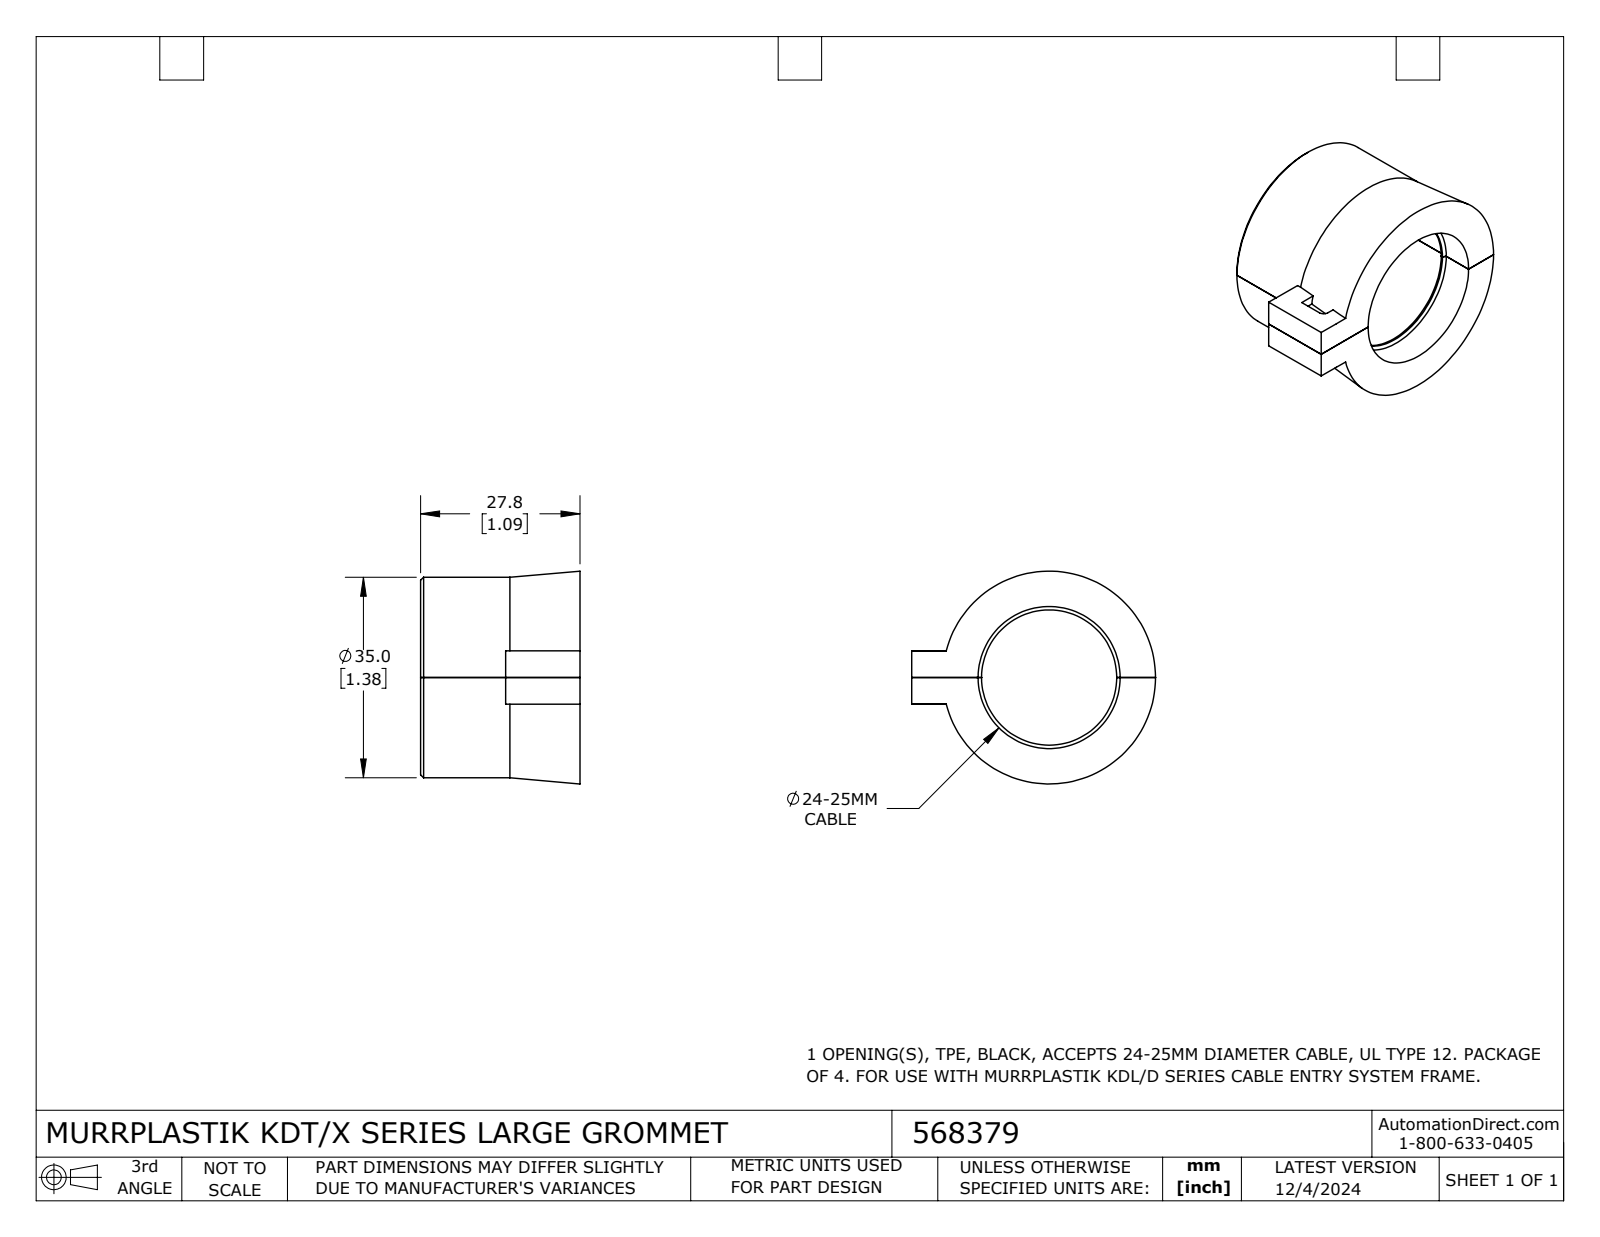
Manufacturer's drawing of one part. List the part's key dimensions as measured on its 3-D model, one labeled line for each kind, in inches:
Part name (STEP PRODUCT): 568379
STEP written by: SolidWorks 2024 (AUTOMOTIVE_DESIGN)
Units: inches
Bodies: 2 solids, 46 faces (22 planar, 14 cylindrical, 10 other)
Overall size (bounding box): 1.676 × 1.462 × 1.094
Volume: 0.902 in³ · Surface area: 11.53 in²
Round holes (diameter × count): ⌀0.929 ×1, ⌀0.976 ×1
Round bosses / shafts (diameter × count): ⌀1.378 ×1
Partial cylindrical surfaces — rounded edges, fillets, slot ends (radius × count): R0.02 ×4, R0.039 ×1
Main face-to-face distances: 1.094, 0.183, 0.366, 0.51, 0.585, 0.061, 0.305, 0.122, 0.157, 0.243
